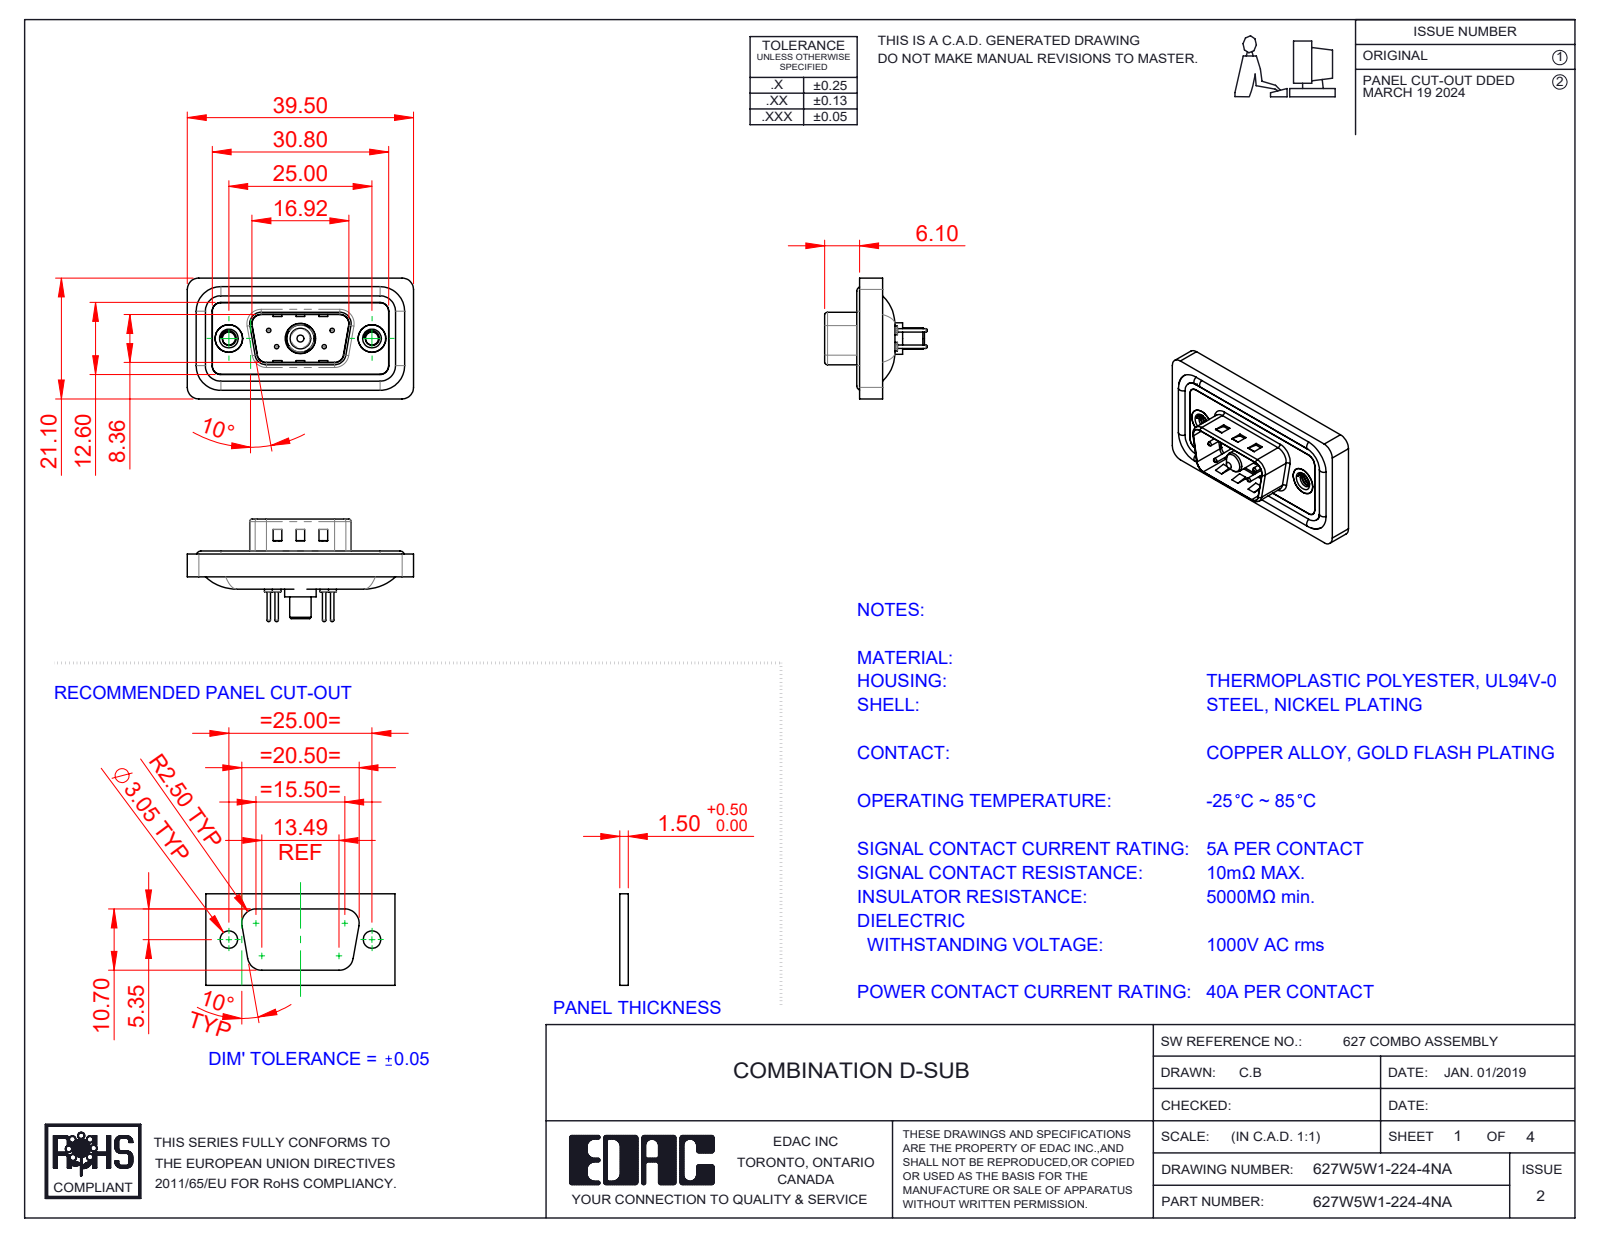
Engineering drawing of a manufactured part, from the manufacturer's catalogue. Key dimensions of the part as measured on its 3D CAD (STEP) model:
Part name (STEP PRODUCT): 627Combo Shell Rear_09 Contacts; 627Combo Waterproof Housing_09 Contacts; 627Combo Housing_5W1; 627W5W1-224-4NA (+5 more)
STEP written by: SolidWorks 2023 (CONFIG_CONTROL_DESIGN)
Units: millimetres
Bodies: 13 solids, 596 faces (183 planar, 257 cylindrical, 156 other)
Overall size (bounding box): 39.5 × 21.1 × 17.9
Volume: 4 408 mm³ · Surface area: 6 950 mm²
Round holes (diameter × count): ⌀0.75 ×4, ⌀1.6 ×4, ⌀2 ×4, ⌀2.26 ×2, ⌀4 ×2, ⌀4.8 ×2, ⌀5 ×2, ⌀4.85 ×1, ⌀5.3 ×1
Round bosses / shafts (diameter × count): ⌀1.6 ×4, ⌀1.5 ×4, ⌀0.6 ×4, ⌀4.9 ×2, ⌀5.5 ×1, ⌀5.2 ×1, ⌀4.75 ×1, ⌀3.75 ×1
Partial cylindrical surfaces — rounded edges, fillets, slot ends (radius × count): R1.5 ×22, R2 ×18, R0.5 ×8, R1.6 ×8, R0.25 ×4, R0.6 ×4, R0.65 ×4, R0.9 ×4
Main face-to-face distances: 0.4, 1.1, 2.9, 1.6, 3.1, 0.5, 1.5, 2.5, 4, 0.8
Hole centre spacings: 3.16, 5.72, 7.1, 12.5, 18.1, 4.39, 4.4, 8.31
